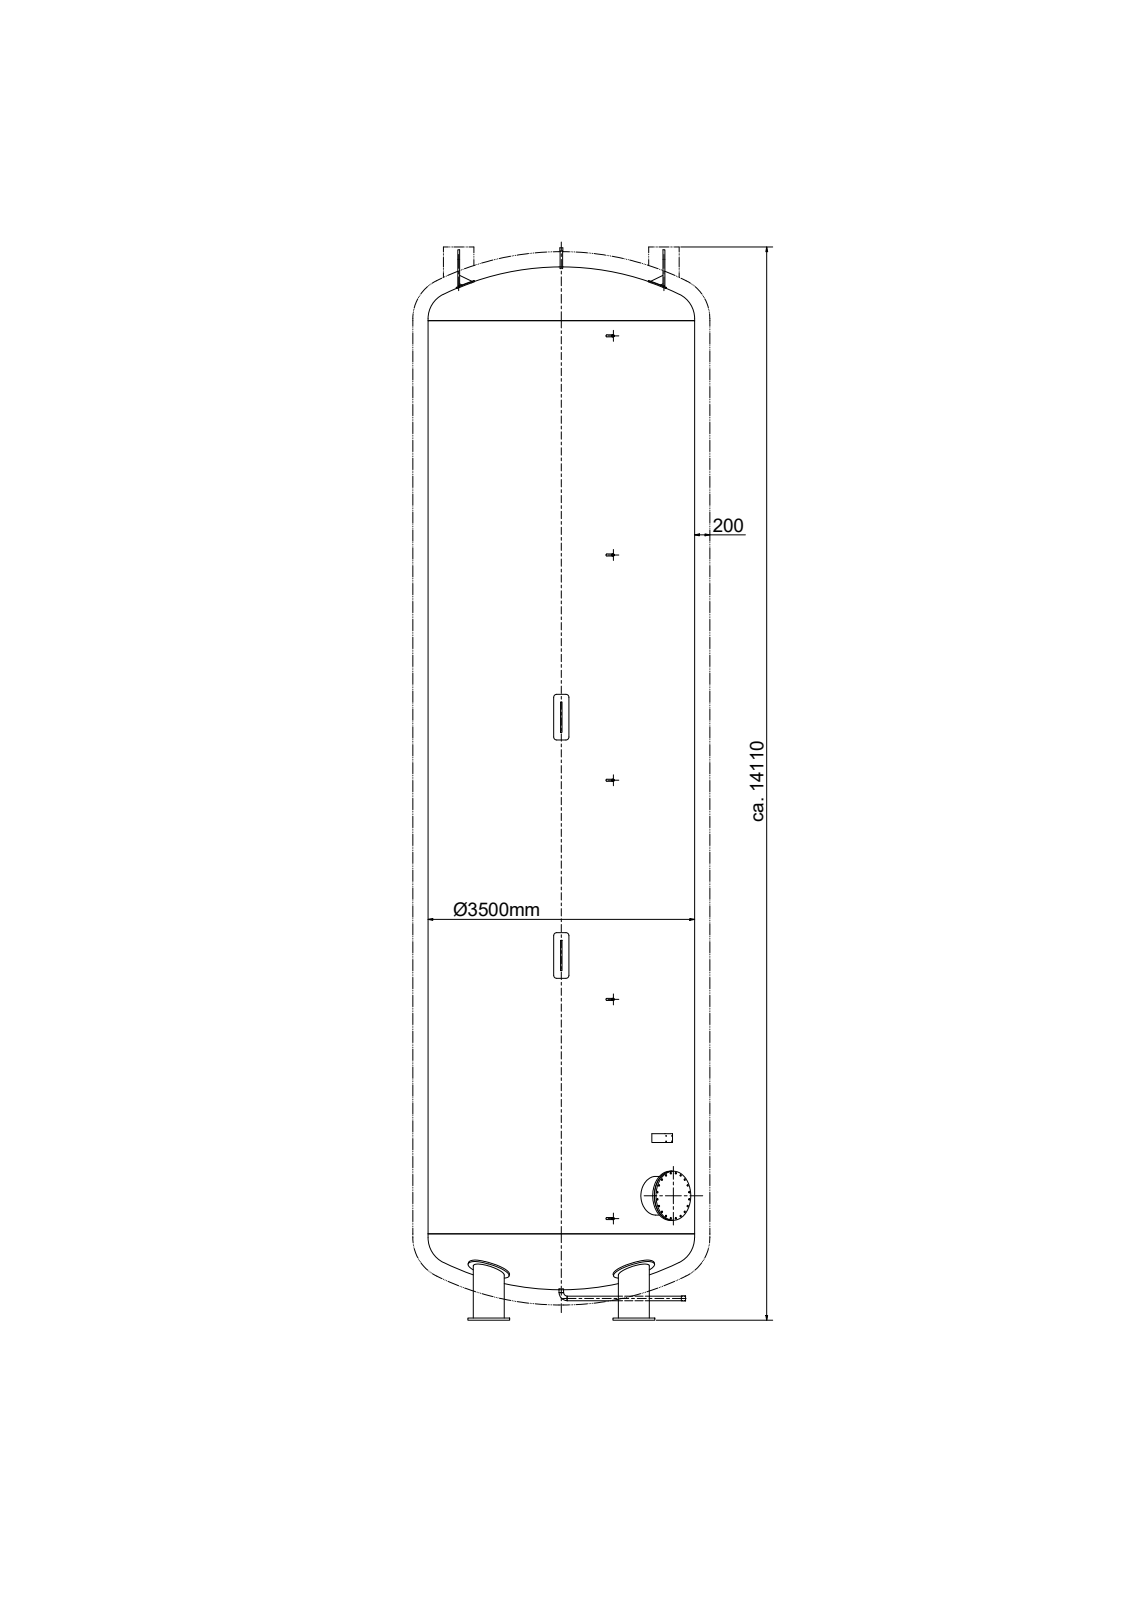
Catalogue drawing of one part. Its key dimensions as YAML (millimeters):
part_name: "Ø3500_123_3_200_RF_WZ2; Klöpper_Gew_Ø3500_6,4; Klöpper_Gew_Ø3500_13,0; Zyl_Ø3500_8x12000_2019 (+8 more)"
step_written_by: "Autodesk Inventor 2019 (AUTOMOTIVE_DESIGN)"
units: millimeters
bodies: {solids: 58, faces: 453, planar: 176, cylindrical: 231, other: 46}
overall_size: [14092.54, 3642, 3500]
volume: 1767000000
surface_area: 343700000
round_holes:
  - {diameter: 22, count: 80}
  - {diameter: 24, count: 16}
  - {diameter: 18.63, count: 5}
  - {diameter: 21.7, count: 5}
  - {diameter: 26.9, count: 5}
  - {diameter: 5.8, count: 4}
  - {diameter: 206.5, count: 4}
  - {diameter: 207.3, count: 4}
  - {diameter: 219.1, count: 4}
  - {diameter: 388.8, count: 4}
  - {diameter: 52.3, count: 2}
  - {diameter: 72, count: 2}
round_bosses_or_shafts:
  - {diameter: 219.1, count: 8}
  - {diameter: 26.9, count: 5}
  - {diameter: 26.4, count: 5}
  - {diameter: 560, count: 4}
  - {diameter: 406.4, count: 4}
  - {diameter: 340, count: 4}
  - {diameter: 268, count: 4}
  - {diameter: 645, count: 2}
partial_cylinders:
  - {radius: 40, count: 8}
  - {radius: 42, count: 8}
  - {radius: 5, count: 2}
  - {radius: 10, count: 2}
  - {radius: 72, count: 2}
  - {radius: 125, count: 1}
  - {radius: 1762, count: 1}
face_to_face_distances: [30, 600, 5555, 6445, 6691.33, 7581.33, 6661.33, 7551.33, 890, 28]
hole_center_spacings: [300, 147.5, 93.86, 185.41, 352.67, 592.61, 485.41, 2880]
